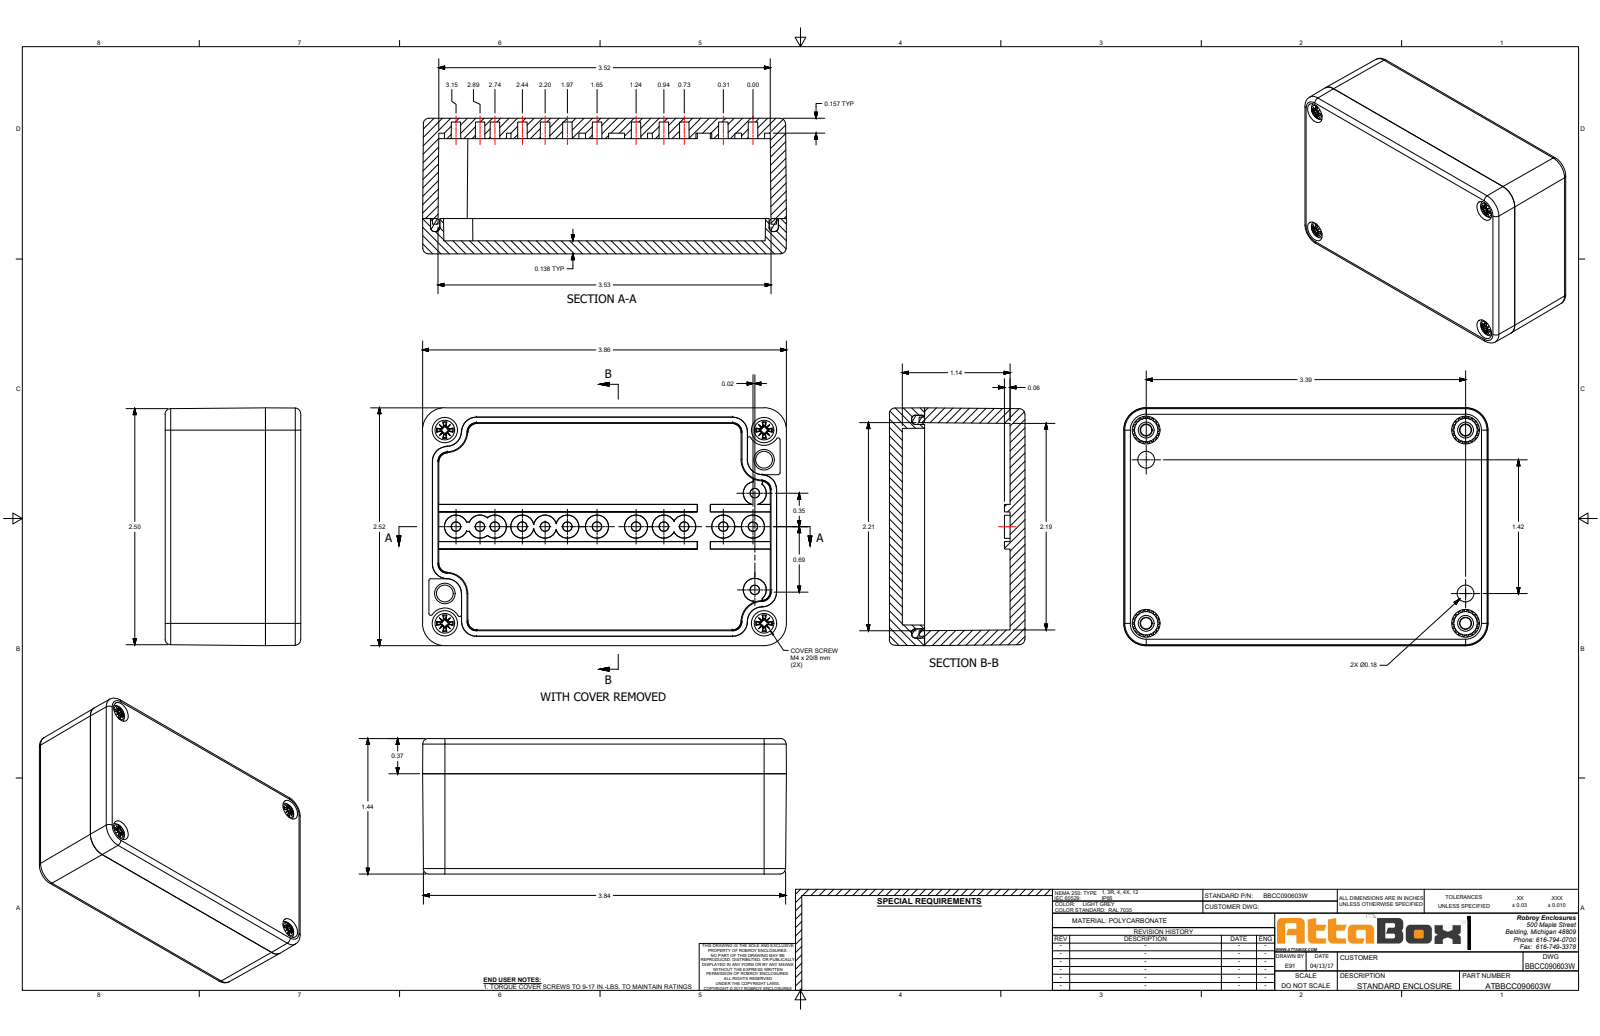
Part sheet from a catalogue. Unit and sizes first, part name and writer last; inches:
Units: inches
Overall size (bounding box): 3.858 × 2.52 × 1.437
Round holes (diameter × count): ⌀0.177 ×6, ⌀0.128 ×4, ⌀0.189 ×4, ⌀0.197 ×4, ⌀0.291 ×4, ⌀0.295 ×4
Round bosses / shafts (diameter × count): ⌀0.268 ×4, ⌀0.173 ×4, ⌀0.157 ×4, ⌀0.13 ×4
Partial cylindrical surfaces — rounded edges, fillets, slot ends (radius × count): R0.043 ×24, R0.039 ×14, R0.02 ×10, R0.059 ×8, R0.098 ×4, R0.102 ×4, R0.124 ×4, R0.138 ×4
Main face-to-face distances: 0.157, 1.437, 0.138, 1.299, 1.142, 1.28, 0.906, 0.236, 0.374, 1.063
Hole centre spacings: 0.315, 1.732, 2.047, 3.386, 3.4, 3.803, 3.957, 3.67
Volume: 5.396 in³ · Surface area: 90.2 in²
Bodies: 11 solids, 1530 faces (581 planar, 332 cylindrical, 617 other)
Part name (STEP PRODUCT): BBCC090603W
STEP written by: SolidWorks 2018 (AUTOMOTIVE_DESIGN)
